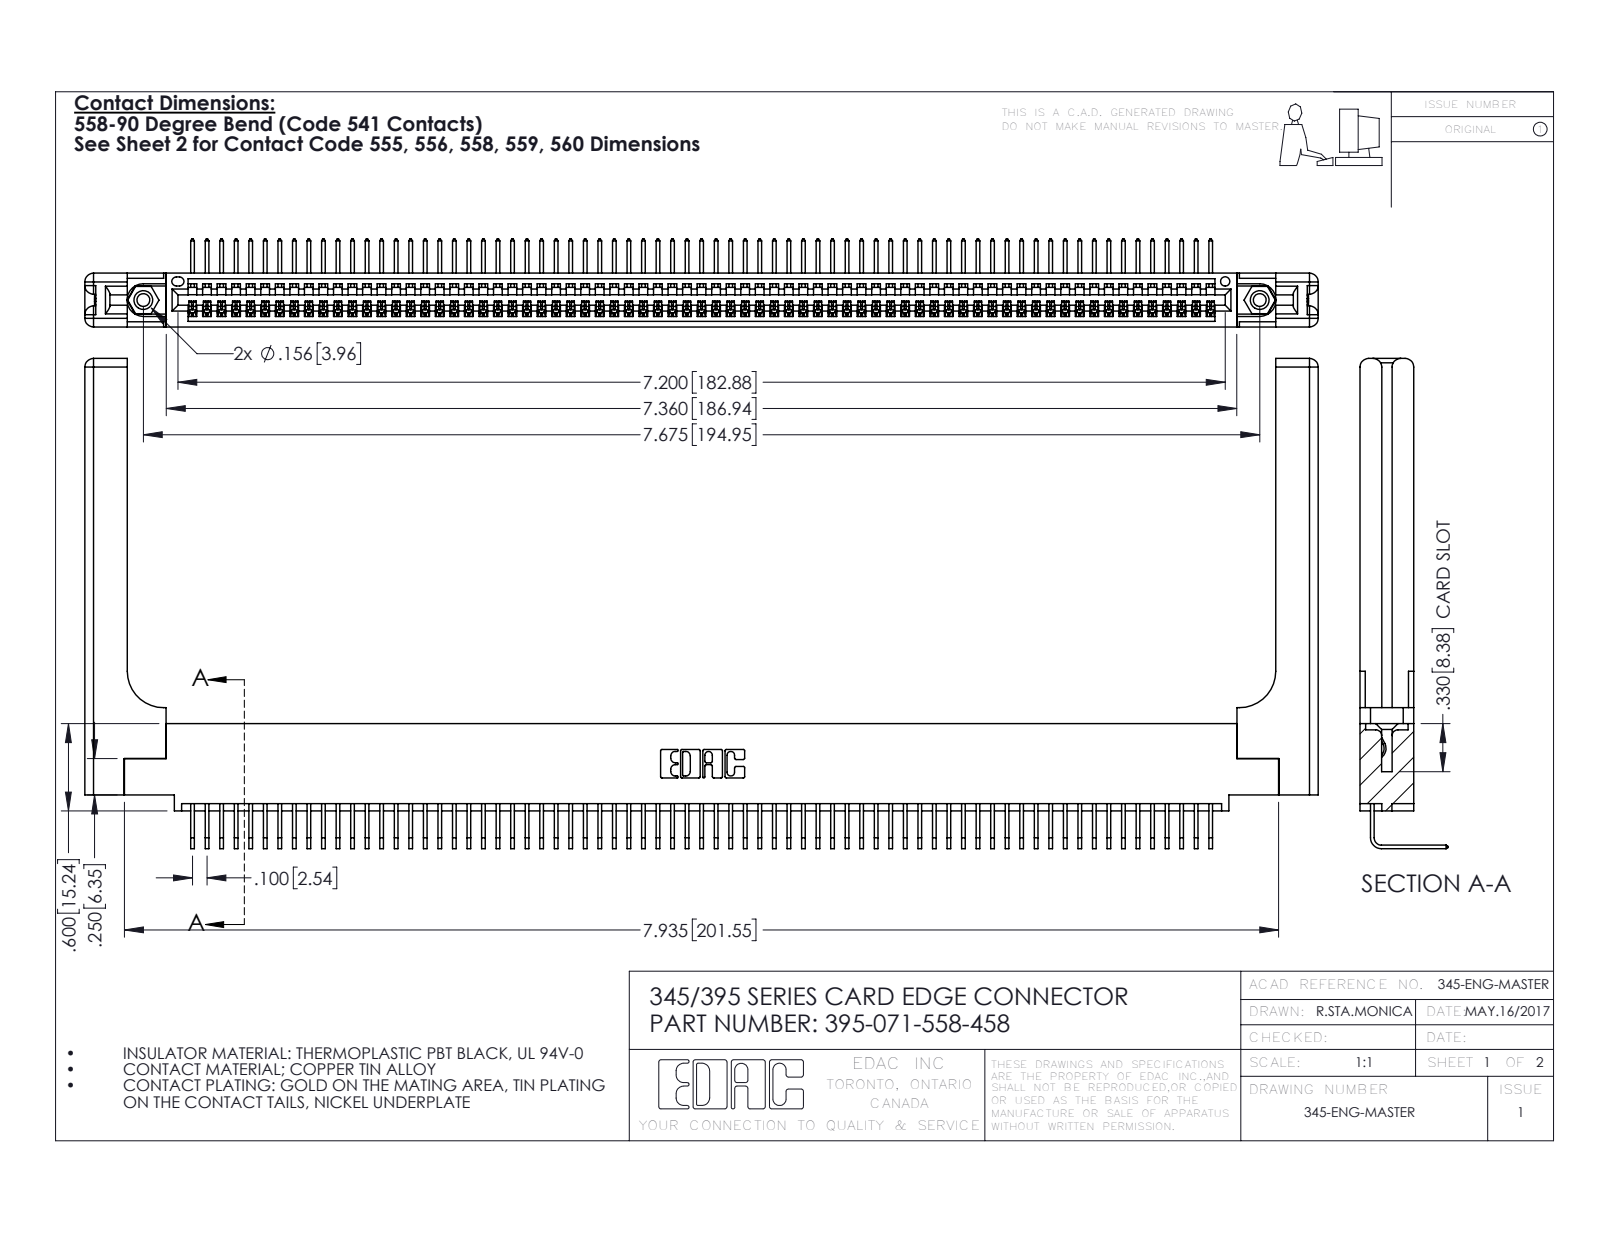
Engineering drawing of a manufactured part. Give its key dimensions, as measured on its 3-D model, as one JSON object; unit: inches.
{"part_name": "345 Part_0.110 Offset - 0.156 Dia-TH; 345-250-001_345-250-001-102; 345-220-058_345-220-058; 395-071-558-458 (+1 more)", "step_written_by": "SolidWorks 2016 (CONFIG_CONTROL_DESIGN)", "units": "inches", "bodies": {"solids": 76, "faces": 4646, "planar": 3214, "cylindrical": 1372, "other": 60}, "overall_size": [8.479, 3.369, 0.605], "volume_in3": 1.792, "surface_area_in2": 54.08, "round_holes": [[0.089, 2], [0.125, 2], [0.156, 2], [0.064, 1]], "round_bosses_or_shafts": [[0.155, 2]], "partial_cylinders_radius": [[0.006, 142], [0.01, 22], [0.06, 16], [0.007, 6], [0.031, 6], [0.026, 3], [0.03, 2], [0.031, 2]], "face_to_face_distances": [0.072, 0.298, 0.37, 0.098, 0.272, 0.025, 0.2, 0.225, 0.148, 0.15], "hole_center_spacings": [0.27, 7.439, 7.675]}
